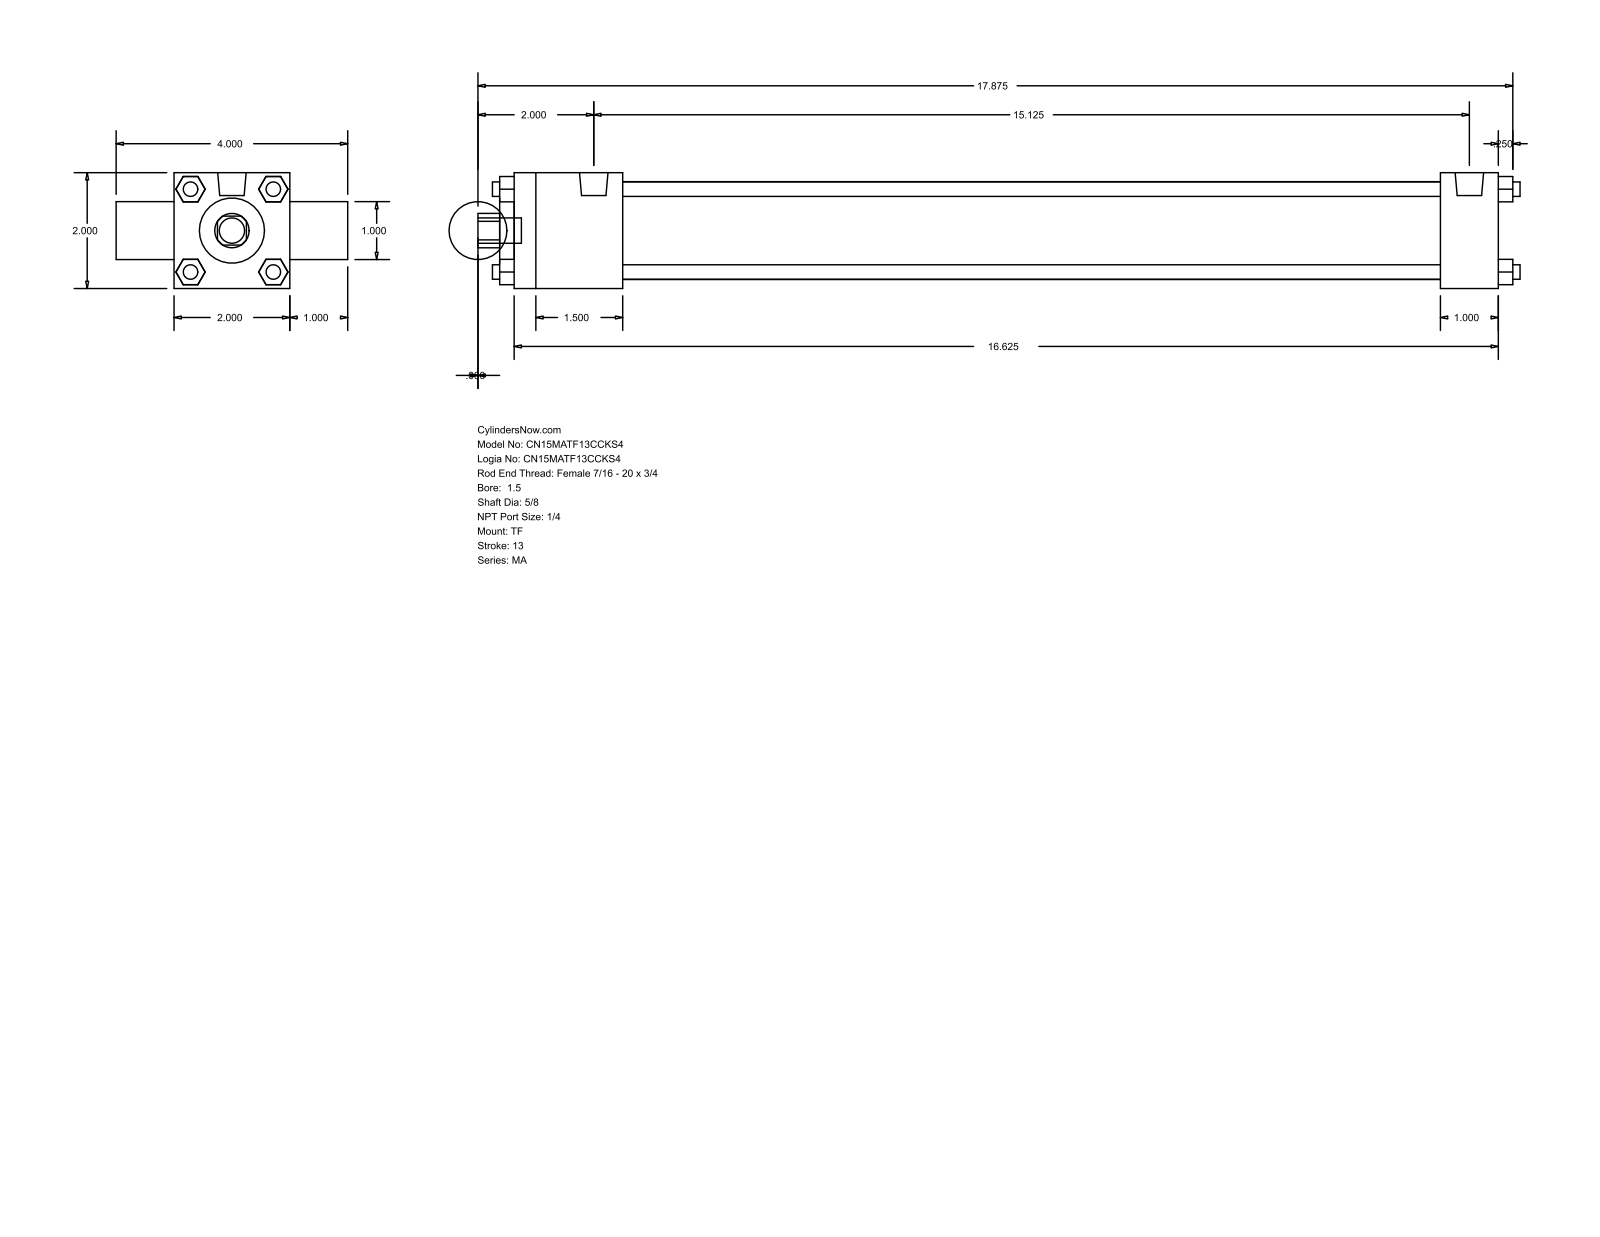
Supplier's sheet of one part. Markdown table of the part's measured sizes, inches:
| quantity | value |
| --- | --- |
| part name | MA_TF__0150_0.625 |
| STEP written by | GSSL Pune (CONFIG_CONTROL_DESIGN) |
| units | inches |
| bodies | 0 solids, 120 faces (92 planar, 28 cylindrical, 0 other) |
| overall size | 18 × 4 × 2 |
| round holes (diameter × count) | 0.625 × 1, 1 × 1, 1.125 × 1, 1.69 × 1 |
| round bosses / shafts (diameter × count) | 0.25 × 4, 0.313 × 3, 0.492 × 2, 0.437 × 1 |
| partial cylindrical surfaces (radius × count) | 0.297 × 1 |
| main face-to-face distances | 2, 17, 1, 3, 1.875, 16, 14.125, 15.125, 1, 17.25 |
